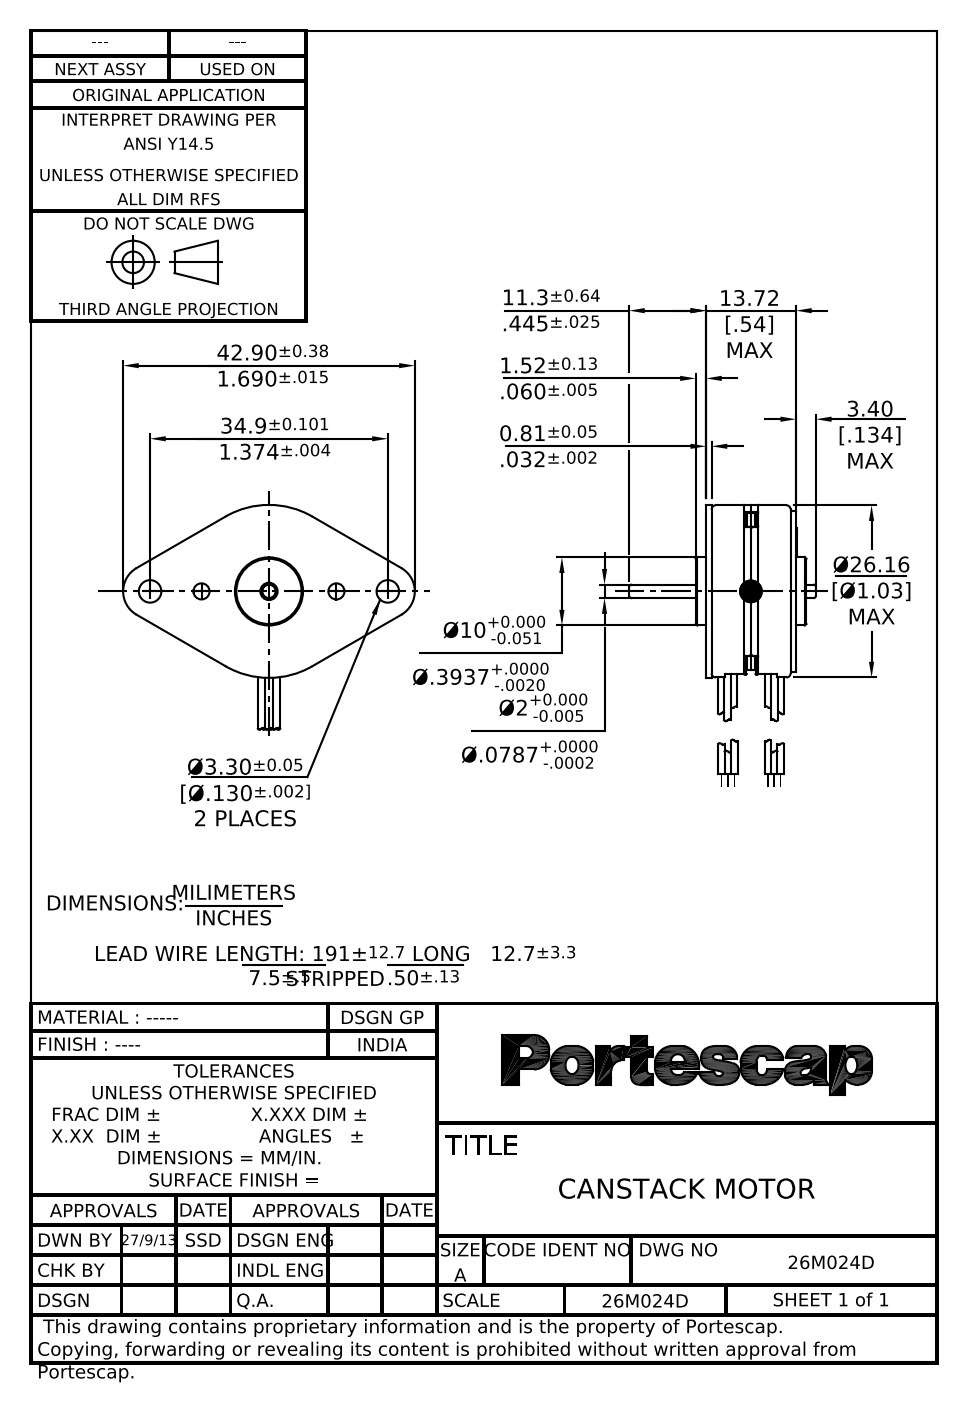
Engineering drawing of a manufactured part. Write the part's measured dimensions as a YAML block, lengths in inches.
part_name: "26M024B1B_ASM"
step_written_by: "PRO/ENGINEER BY PARAMETRIC TECHNOLOGY CORPORATION, 2014310 (CONFIG_CONTROL_DESIGN)"
units: inches
bodies: {solids: 1, faces: 280, planar: 135, cylindrical: 108, other: 37}
overall_size: [1.686, 1.353, 1.08]
volume: 0.426
surface_area: 5.043
round_holes:
  - {diameter: 0.093, count: 6}
  - {diameter: 0.039, count: 4}
  - {diameter: 0.13, count: 2}
  - {diameter: 0.079, count: 1}
  - {diameter: 1.001, count: 1}
round_bosses_or_shafts:
  - {diameter: 0.037, count: 6}
  - {diameter: 0.995, count: 1}
  - {diameter: 0.928, count: 1}
  - {diameter: 0.394, count: 1}
  - {diameter: 0.079, count: 1}
partial_cylinders:
  - {radius: 0.01, count: 10}
  - {radius: 0.039, count: 4}
  - {radius: 0.156, count: 2}
  - {radius: 0.482, count: 1}
  - {radius: 0.495, count: 1}
  - {radius: 0.5, count: 1}
face_to_face_distances: [0.52, 0.032, 0.488, 0.06, 0.58, 0.548, 0.092, 0.64, 0.057, 0.491]
hole_center_spacings: [0.39, 0.112, 0.297, 0.359, 0.425, 0.431, 0.535, 0.616]
